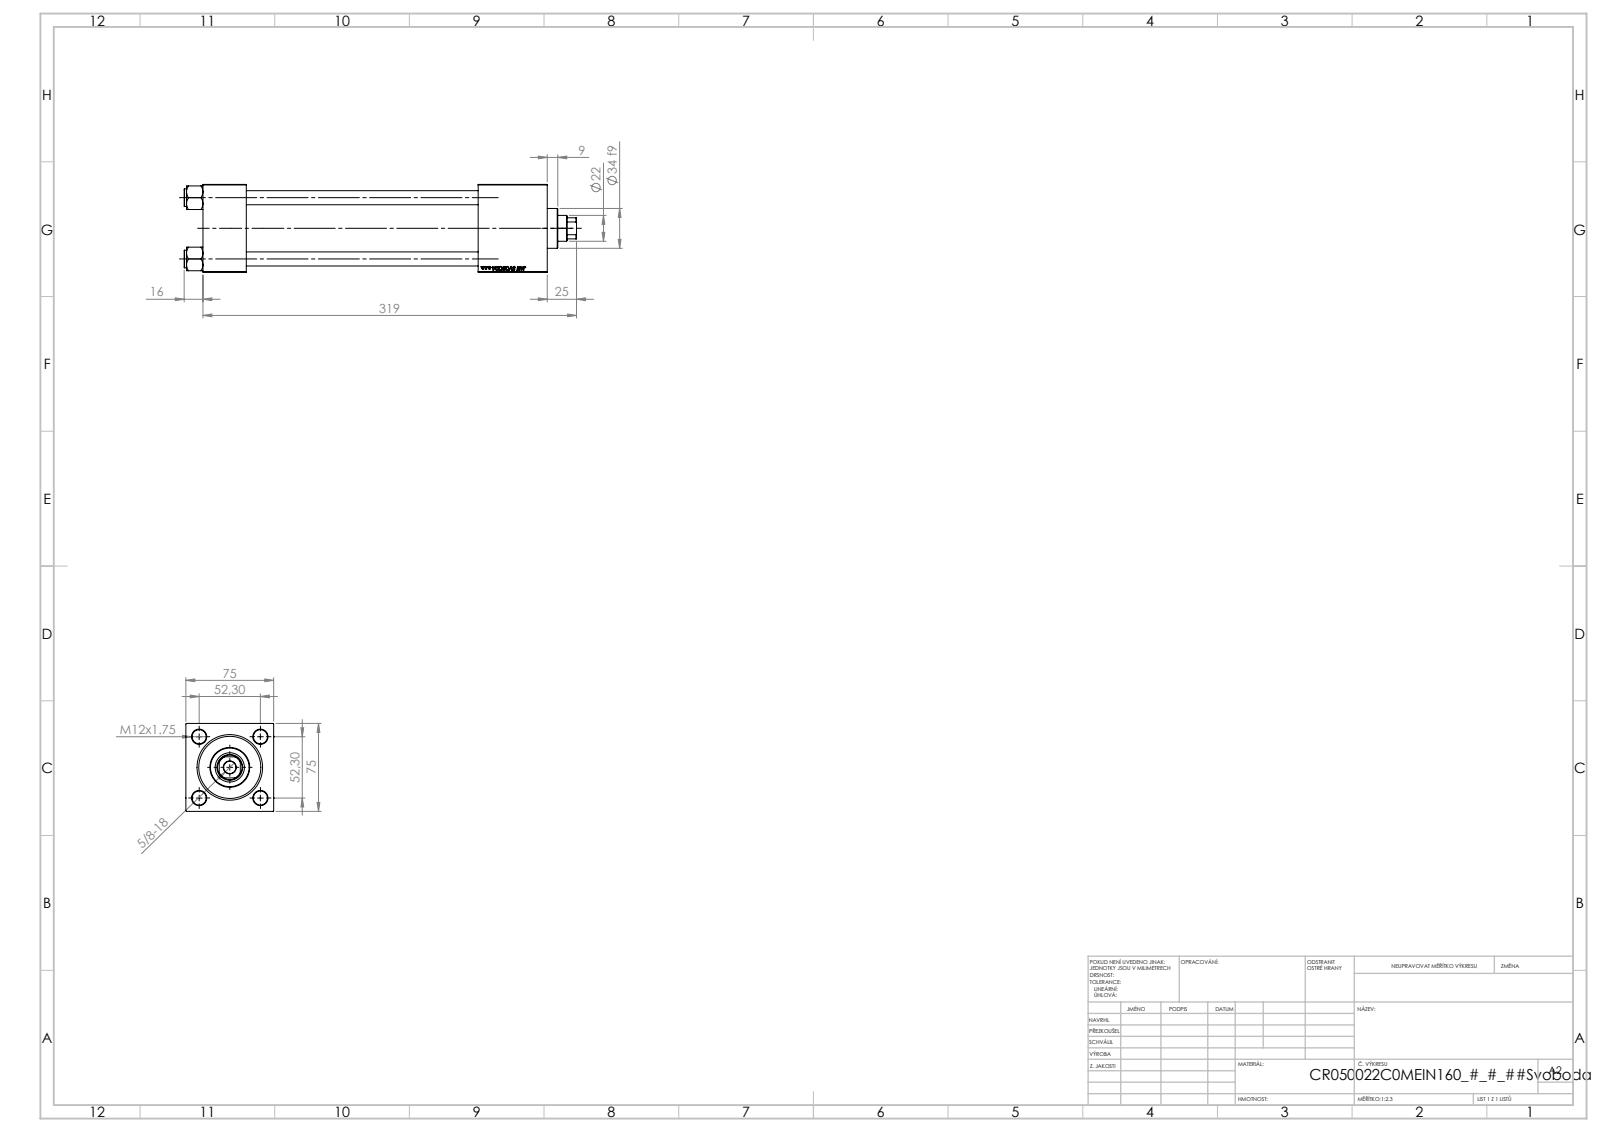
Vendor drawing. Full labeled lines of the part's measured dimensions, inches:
Part name (STEP PRODUCT): NUT_M5_C; V215CR_C_TYCINKA; V215_VC_A; V215CR_C_Body (+1 more)
STEP written by: SolidWorks 2019 (CONFIG_CONTROL_DESIGN)
Units: inches
Bodies: 11 solids, 1149 faces (526 planar, 87 cylindrical, 536 other)
Overall size (bounding box): 13.189 × 2.974 × 2.953
Volume: 51.46 in³ · Surface area: 348.3 in²
Round holes (diameter × count): ⌀0.472 ×4, ⌀0.276 ×2, ⌀0.825 ×2, ⌀1.181 ×2, ⌀0.413 ×1, ⌀0.866 ×1, ⌀0.984 ×1, ⌀1.614 ×1, ⌀1.969 ×1, ⌀2.087 ×1
Round bosses / shafts (diameter × count): ⌀0.591 ×4, ⌀2.205 ×1, ⌀1.339 ×1
Partial cylindrical surfaces — rounded edges, fillets, slot ends (radius × count): R0.413 ×1
Main face-to-face distances: 2.953, 1.457, 11.575, 10.118, 9.252, 7.795, 2.323, 10.445, 8.988, 1.193
Hole centre spacings: 1.456, 2.059, 2.912, 9.193
